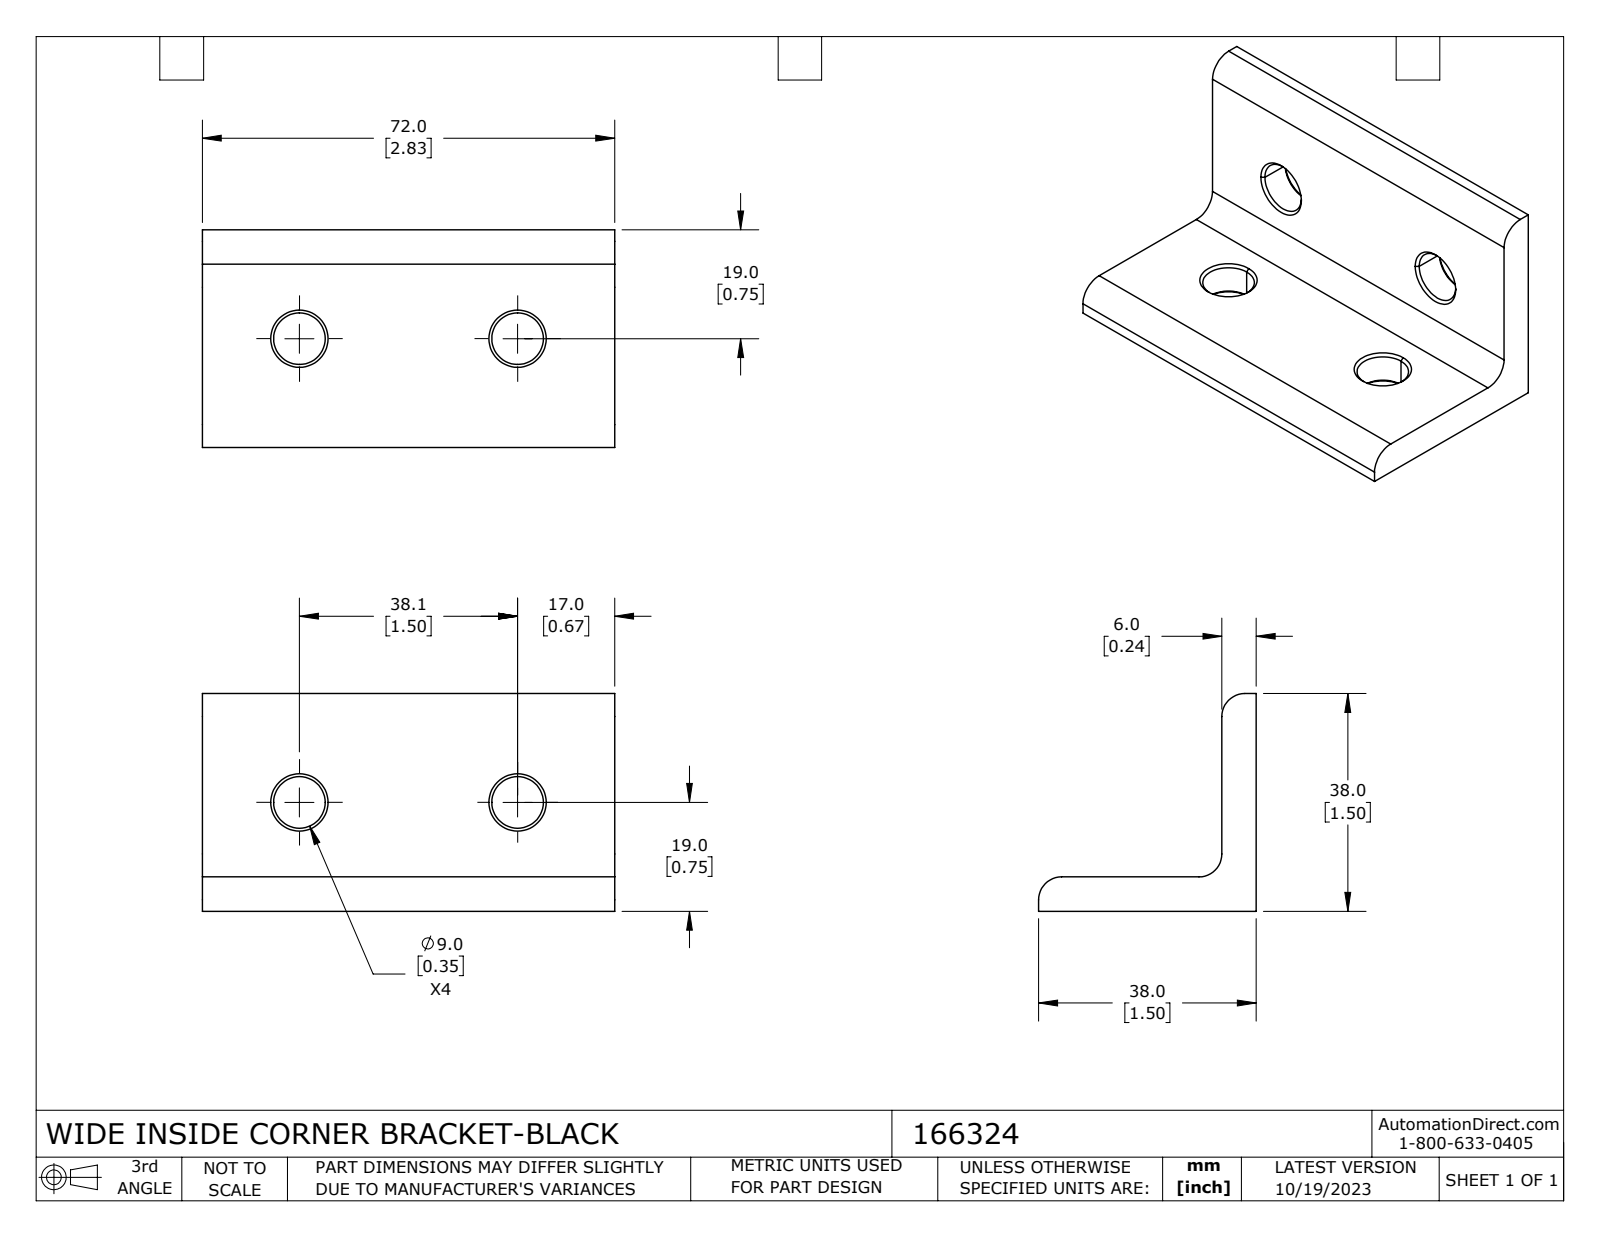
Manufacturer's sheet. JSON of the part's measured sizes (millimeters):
{"part_name": "166324", "step_written_by": "SolidWorks 2023 (CONFIG_CONTROL_DESIGN)", "units": "millimeters", "bodies": {"solids": 1, "faces": 35, "planar": 8, "cylindrical": 11, "other": 16}, "overall_size": [72, 38, 38], "volume_mm3": 28437, "surface_area_mm2": 11512, "round_holes": [[9, 4]], "partial_cylinders_radius": [[4, 3]], "face_to_face_distances": [6, 72, 38, 32], "hole_center_spacings": [38.1]}
